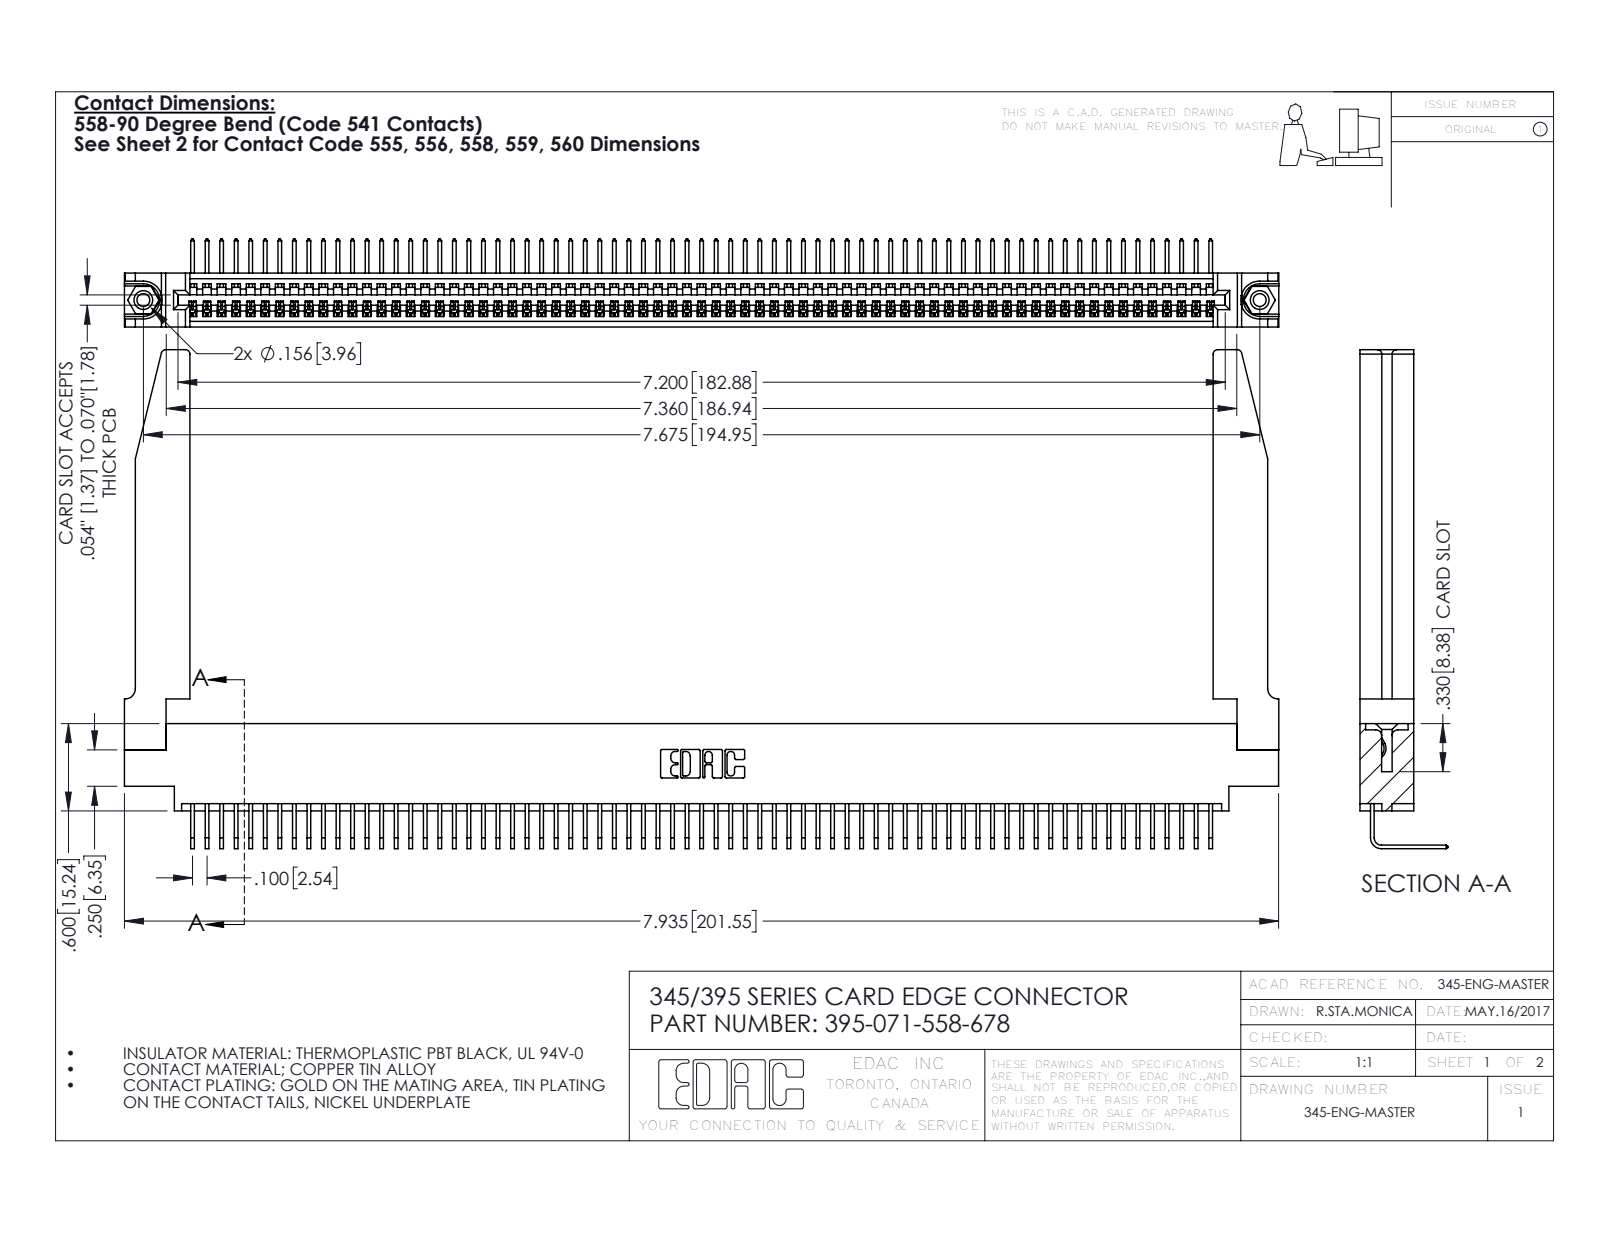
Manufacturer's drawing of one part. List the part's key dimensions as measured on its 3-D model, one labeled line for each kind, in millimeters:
Part name (STEP PRODUCT): 345 Part_0.170 Offset - 0.156 Dia-TH; 395-071-558-678; 345-220-078_345-220-078; 345-292-001_558 Tail - 2 (+1 more)
STEP written by: SolidWorks 2016 (CONFIG_CONTROL_DESIGN)
Units: millimetres
Bodies: 76 solids, 4624 faces (3208 planar, 1364 cylindrical, 52 other)
Overall size (bounding box): 201.6 × 87.1 × 15.4
Volume: 27 280 mm³ · Surface area: 34 680 mm²
Round holes (diameter × count): ⌀2.3 ×2, ⌀3.2 ×2, ⌀4 ×2, ⌀1.6 ×1
Round bosses / shafts (diameter × count): ⌀3.9 ×2
Partial cylindrical surfaces — rounded edges, fillets, slot ends (radius × count): R0.2 ×142, R0.3 ×22, R0.8 ×8, R0.2 ×6, R0.8 ×6, R0.7 ×3, R0.8 ×2, R1 ×2
Main face-to-face distances: 1.8, 9.4, 7.6, 2.5, 6.9, 0.6, 5.1, 5.7, 4.4, 3.8
Hole centre spacings: 6.9, 189, 194.9
